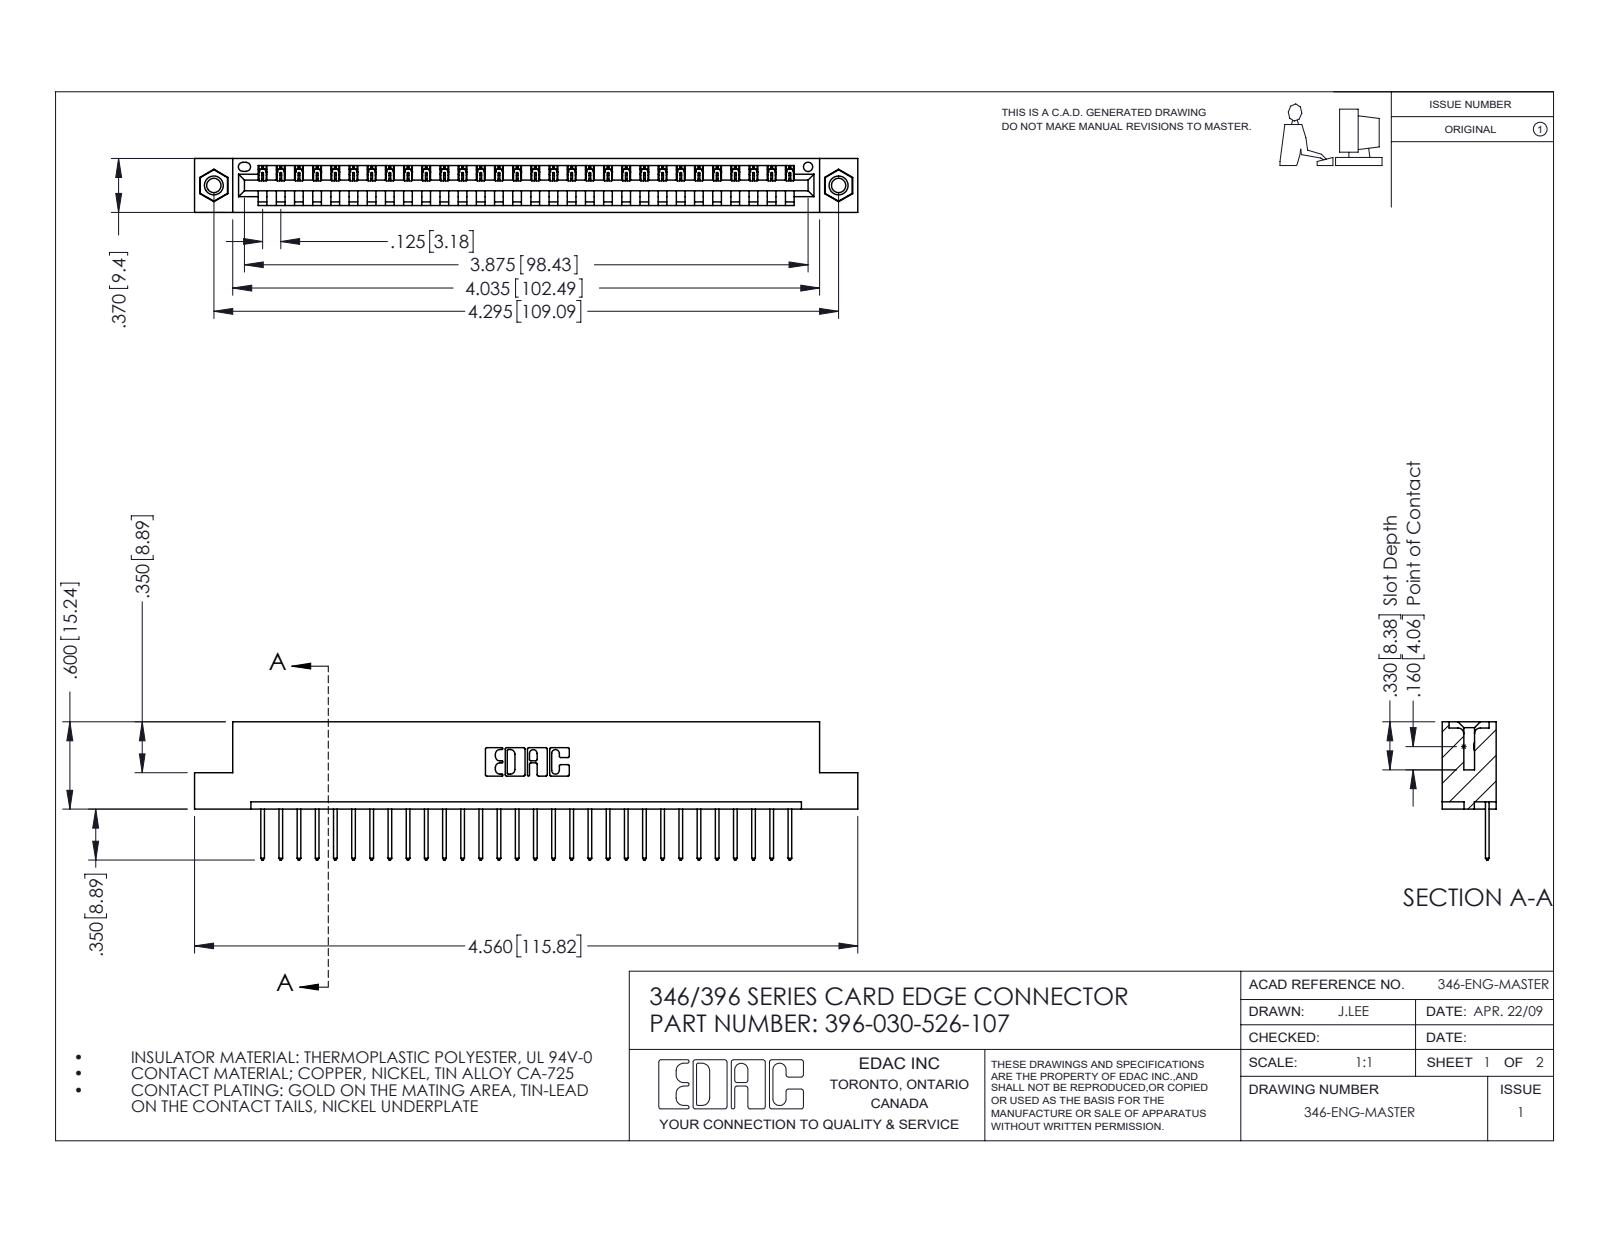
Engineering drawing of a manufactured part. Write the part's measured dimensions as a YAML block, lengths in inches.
part_name: "396-030-526-107; 345-250-001_345-250-005-103; 345-292-001_345-293-126; 346 Part_Flush Mounting Lugs - 0.156 Dia-TI"
step_written_by: "SolidWorks 2016 (CONFIG_CONTROL_DESIGN)"
units: inches
bodies: {solids: 33, faces: 1922, planar: 1308, cylindrical: 598, other: 16}
overall_size: [4.56, 0.95, 0.37]
volume: 0.669
surface_area: 21.05
round_holes:
  - {diameter: 0.098, count: 2}
  - {diameter: 0.125, count: 2}
  - {diameter: 0.156, count: 2}
  - {diameter: 0.064, count: 1}
round_bosses_or_shafts:
  - {diameter: 0.155, count: 2}
partial_cylinders:
  - {radius: 0.006, count: 60}
  - {radius: 0.01, count: 60}
  - {radius: 0.01, count: 22}
  - {radius: 0.007, count: 6}
  - {radius: 0.031, count: 6}
  - {radius: 0.026, count: 3}
  - {radius: 0.031, count: 2}
  - {radius: 0.04, count: 2}
face_to_face_distances: [0.048, 0.322, 0.37, 0.25, 0.072, 0.298, 0.025, 0.148, 0.222, 0.1]
hole_center_spacings: [0.246, 4.087, 4.295]
